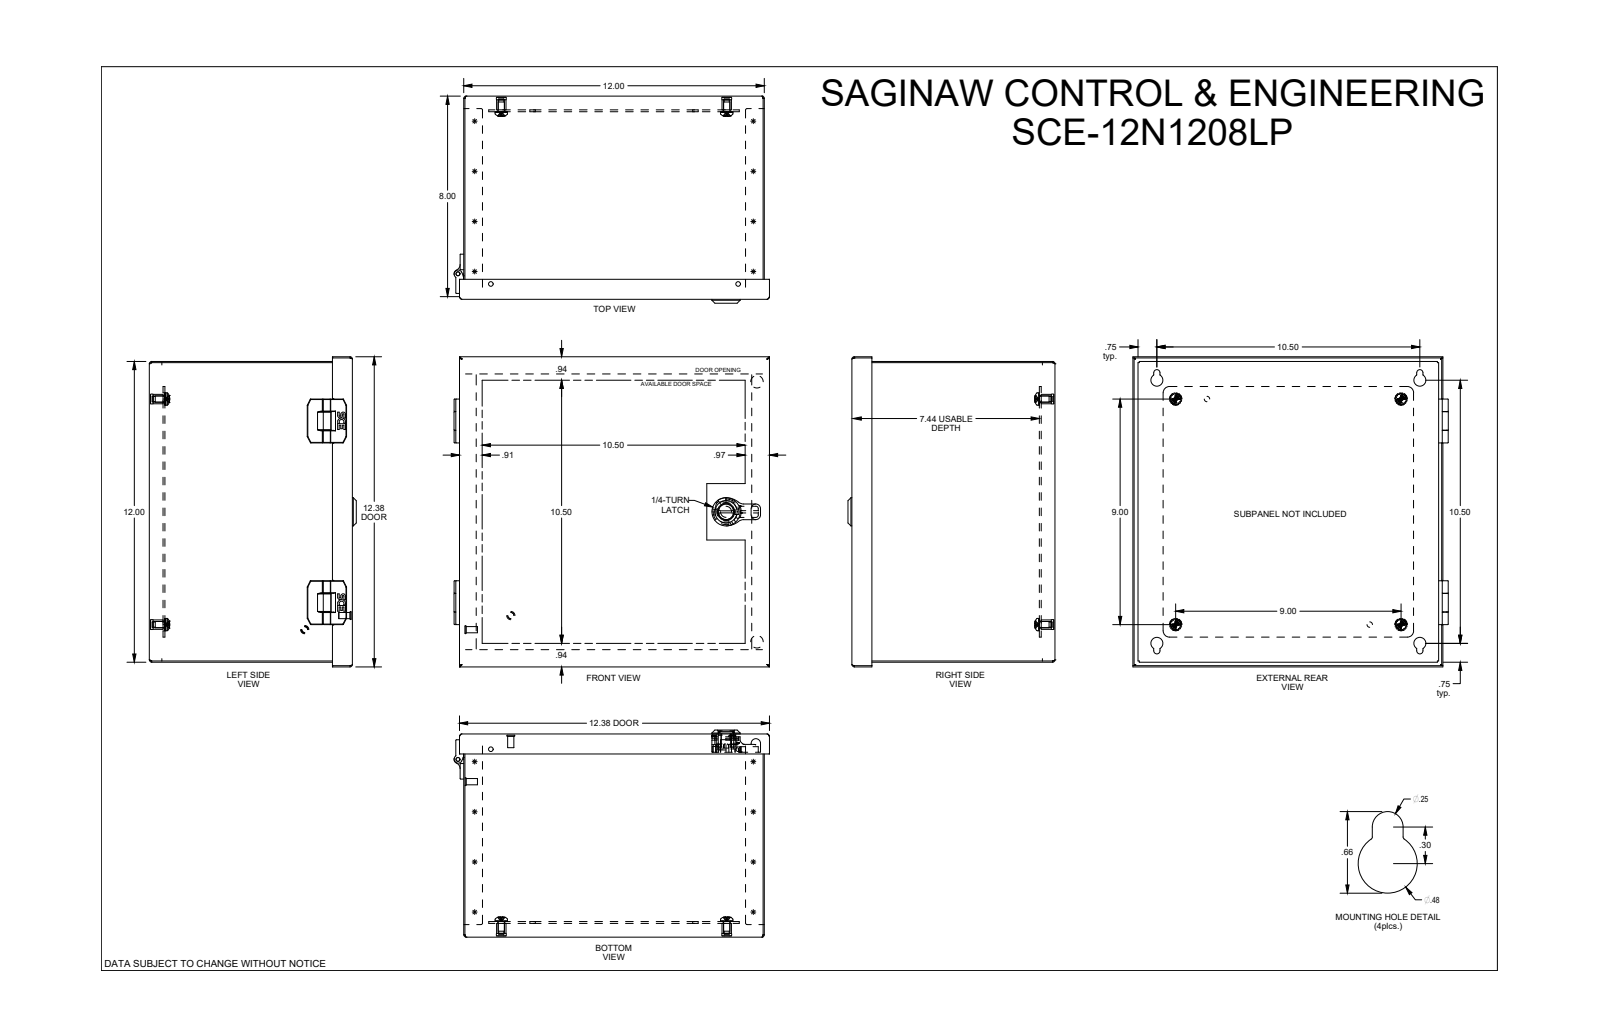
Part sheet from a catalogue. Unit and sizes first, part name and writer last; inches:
Units: inches
Overall size (bounding box): 12.593 × 12.375 × 8.263
Round holes (diameter × count): ⌀0.17 ×4, ⌀0.203 ×4, ⌀0.25 ×4, ⌀0.281 ×4, ⌀0.329 ×4, ⌀0.343 ×4, ⌀0.48 ×4, ⌀0.193 ×3, ⌀0.187 ×2, ⌀0.218 ×2, ⌀0.158 ×1, ⌀0.44 ×1
Round bosses / shafts (diameter × count): ⌀0.248 ×6, ⌀0.492 ×4, ⌀0.479 ×4, ⌀0.376 ×4, ⌀0.237 ×4, ⌀0.16 ×4, ⌀0.5 ×2, ⌀0.323 ×2
Partial cylindrical surfaces — rounded edges, fillets, slot ends (radius × count): R0.01 ×253, R0.02 ×95, R0.06 ×25, R0.015 ×24, R0.025 ×24, R0.055 ×6, R0.25 ×6, R0.125 ×4
Main face-to-face distances: 0.06, 11.94, 8.047, 12, 11.88, 7.987, 8.107, 0.623, 0.563, 7.424
Hole centre spacings: 9.779, 1.061, 7.75, 9, 10.5, 13.789, 1.089, 1.091
Volume: 53.3 in³ · Surface area: 1 714 in²
Bodies: 31 solids, 1529 faces (554 planar, 645 cylindrical, 330 other)
Part name (STEP PRODUCT): SCE-12N1208LP
STEP written by: SolidWorks 2019 (AUTOMOTIVE_DESIGN)
